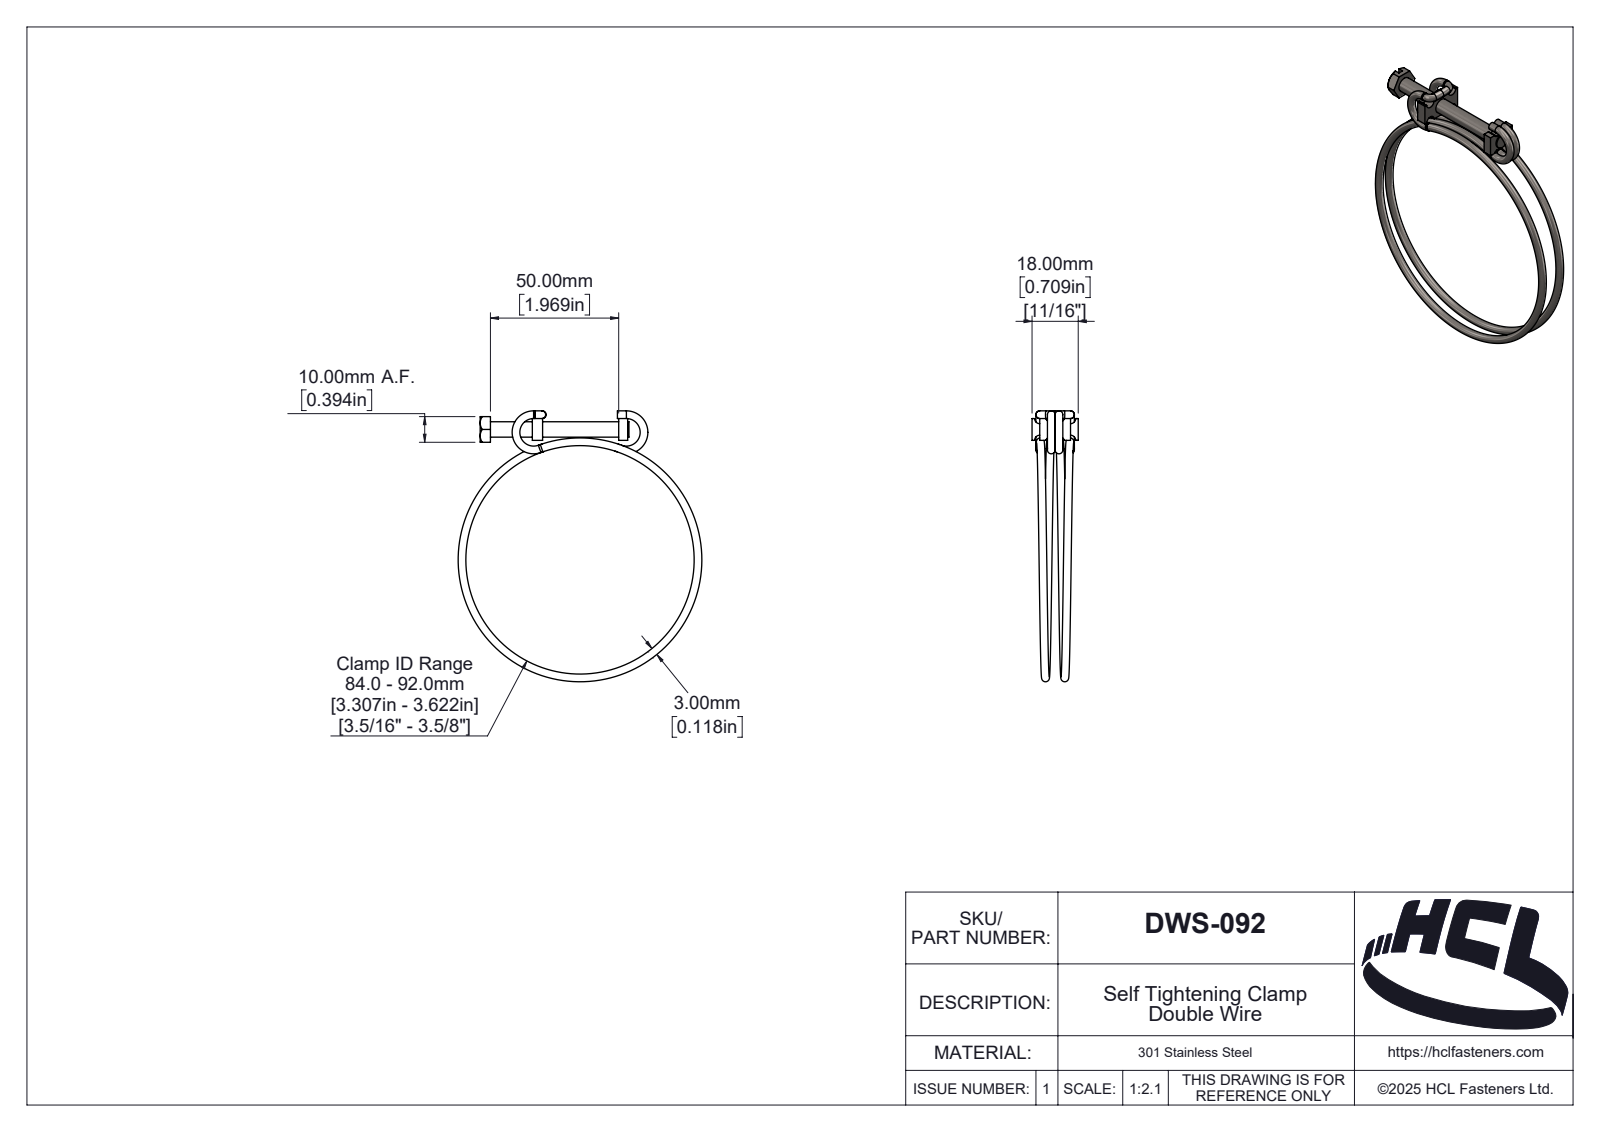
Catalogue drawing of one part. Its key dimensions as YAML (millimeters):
part_name: "DWS-092"
step_written_by: "SolidWorks 2025 (AUTOMOTIVE_DESIGN)"
units: millimeters
bodies: {solids: 6, faces: 213, planar: 55, cylindrical: 74, other: 84}
overall_size: [105.55, 95, 18]
volume: 7821
surface_area: 9430
round_holes:
  - {diameter: 6, count: 1}
round_bosses_or_shafts:
  - {diameter: 3, count: 4}
partial_cylinders:
  - {radius: 0.2, count: 12}
  - {radius: 1, count: 4}
  - {radius: 2, count: 4}
  - {radius: 0.4, count: 1}
  - {radius: 0.51, count: 1}
  - {radius: 0.53, count: 1}
  - {radius: 0.64, count: 1}
  - {radius: 0.91, count: 1}
face_to_face_distances: [4, 20.34, 10, 33.66, 3, 54, 33.16, 53.5, 1, 29.66]
